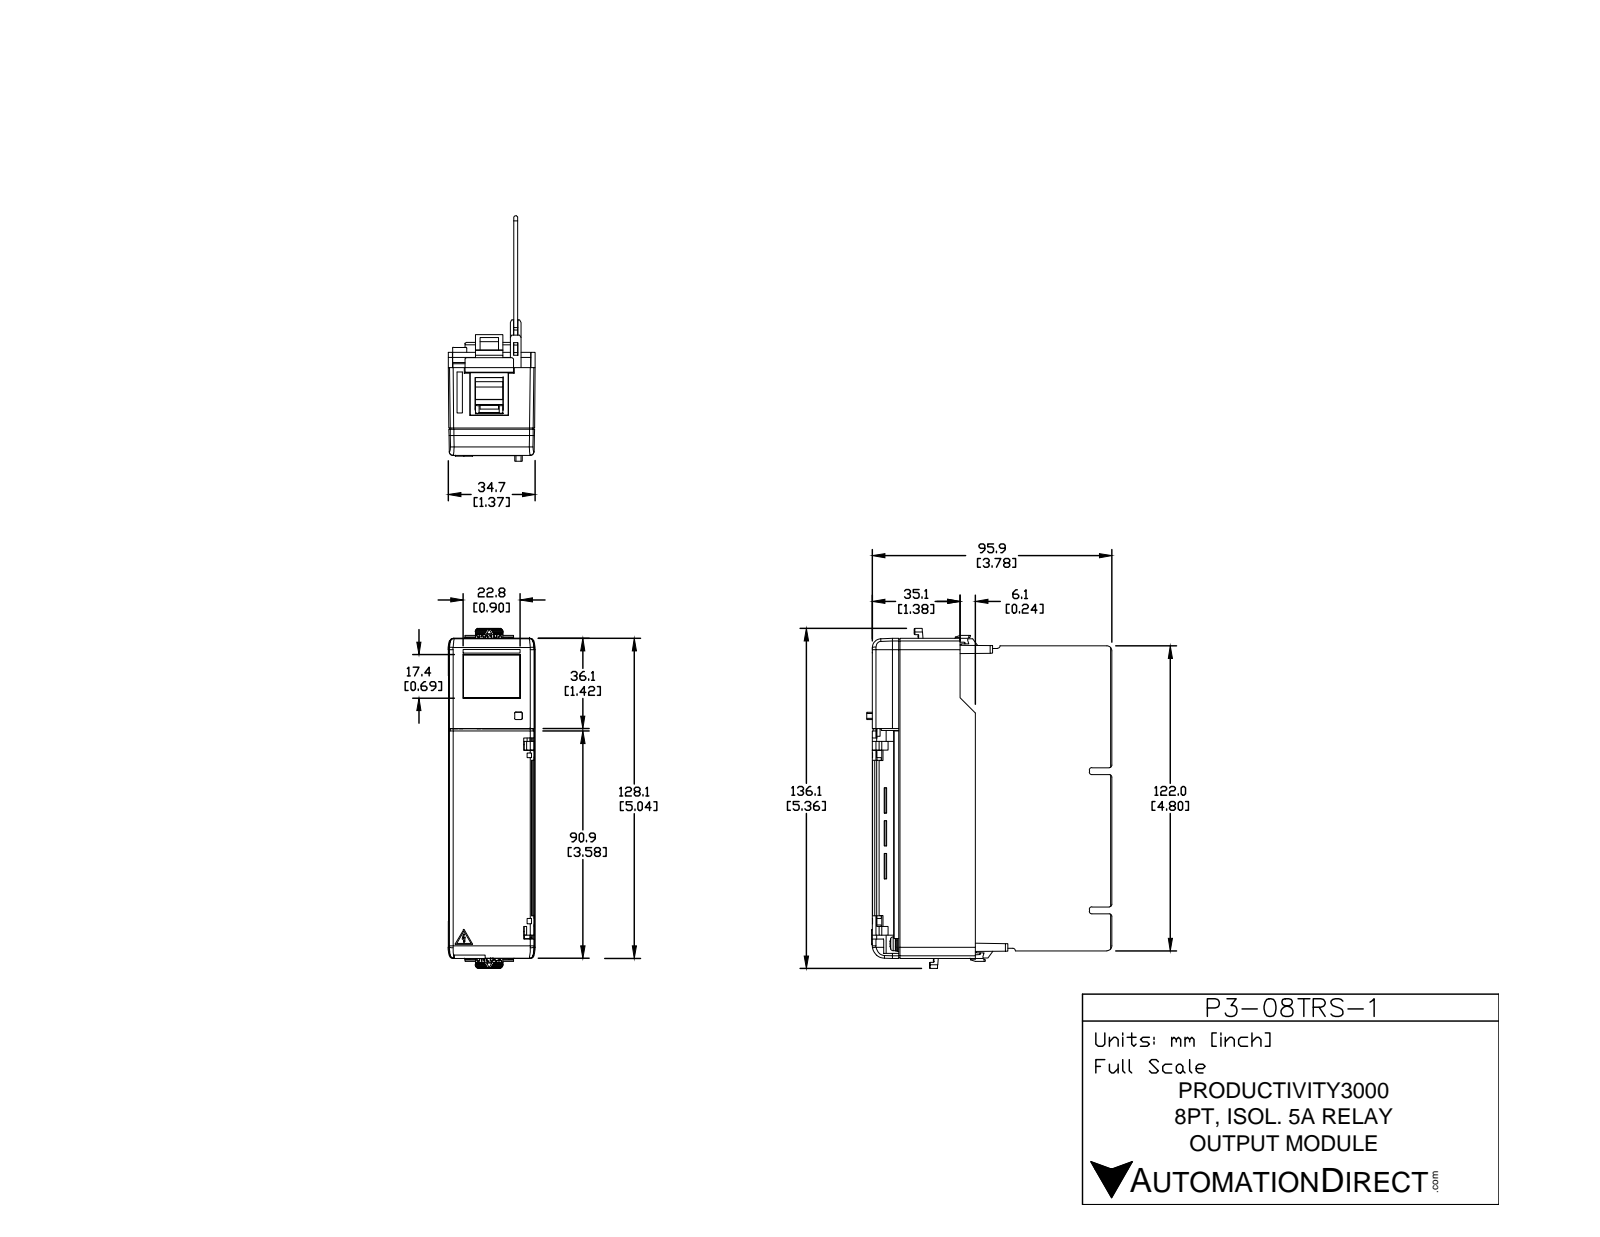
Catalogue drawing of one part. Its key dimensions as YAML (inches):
part_name: "P3-08TRS-1"
step_written_by: "SolidWorks 2009 (CONFIG_CONTROL_DESIGN)"
units: inches
bodies: {solids: 1, faces: 3804, planar: 2821, cylindrical: 737, other: 246}
overall_size: [5.357, 3.787, 1.37]
volume: 6.184
surface_area: 116.9
round_holes:
  - {diameter: 0.126, count: 22}
  - {diameter: 0.197, count: 2}
  - {diameter: 0.071, count: 1}
round_bosses_or_shafts:
  - {diameter: 0.217, count: 22}
  - {diameter: 0.118, count: 22}
  - {diameter: 0.094, count: 20}
  - {diameter: 0.22, count: 2}
  - {diameter: 0.087, count: 2}
  - {diameter: 0.079, count: 2}
  - {diameter: 0.059, count: 1}
partial_cylinders:
  - {radius: 0.02, count: 91}
  - {radius: 0.039, count: 33}
  - {radius: 0.012, count: 29}
  - {radius: 0.066, count: 22}
  - {radius: 0.059, count: 13}
  - {radius: 0.079, count: 6}
  - {radius: 0.008, count: 5}
  - {radius: 0.004, count: 4}
face_to_face_distances: [0.063, 0.067, 1.111, 1.044, 1.282, 0.874, 0.087, 0.311, 0.268, 0.209]
hole_center_spacings: [0.342, 0.3, 0.545, 0.6, 0.811, 0.9, 1.094, 1.2]
